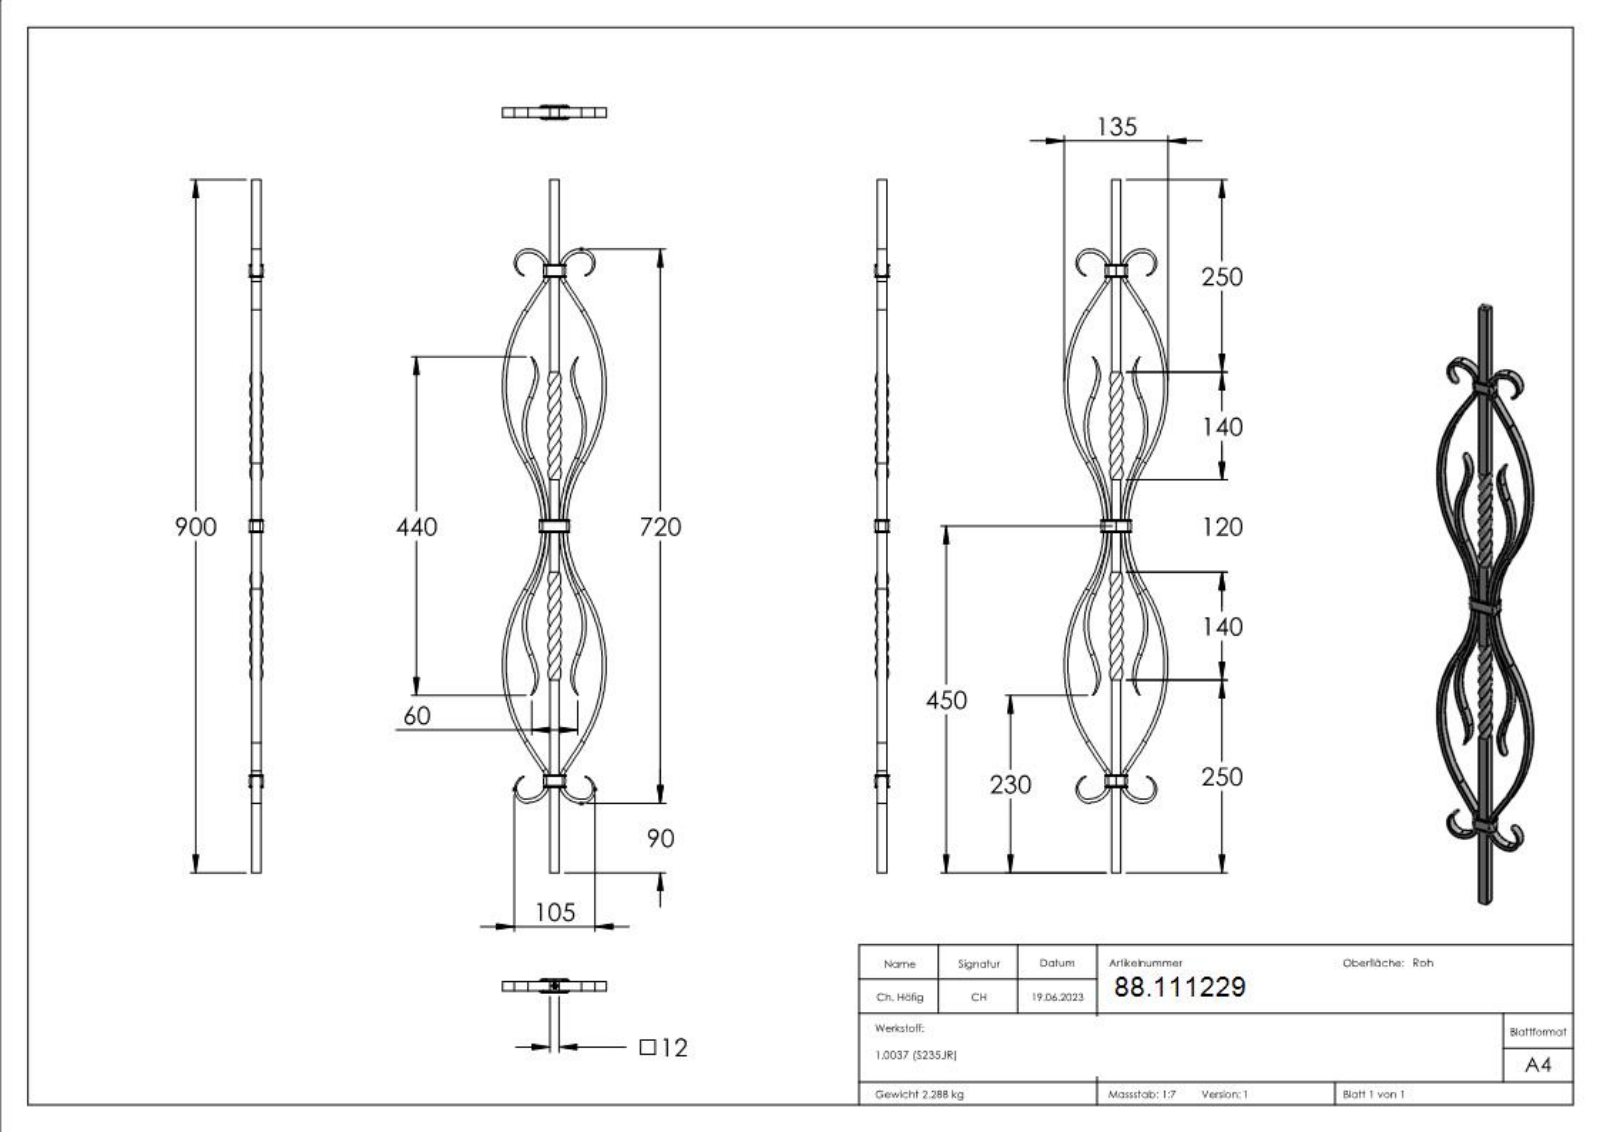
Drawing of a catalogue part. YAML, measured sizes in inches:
part_name: "1229"
step_written_by: "SolidWorks 2018 (CONFIG_CONTROL_DESIGN)"
units: inches
bodies: {solids: 10, faces: 797, planar: 337, cylindrical: 239, other: 221}
overall_size: [35.433, 5.315, 0.709]
volume: 17.9
surface_area: 222.8
partial_cylinders:
  - {radius: 0.02, count: 72}
  - {radius: 0.008, count: 24}
  - {radius: 0.851, count: 12}
  - {radius: 0.039, count: 8}
  - {radius: 0.157, count: 8}
  - {radius: 0.236, count: 8}
  - {radius: 3.74, count: 8}
  - {radius: 0.928, count: 4}
face_to_face_distances: [0.472, 13.048, 0.689, 0.217, 0.63, 0.315, 26.096, 0.197, 13.363, 13.678]
